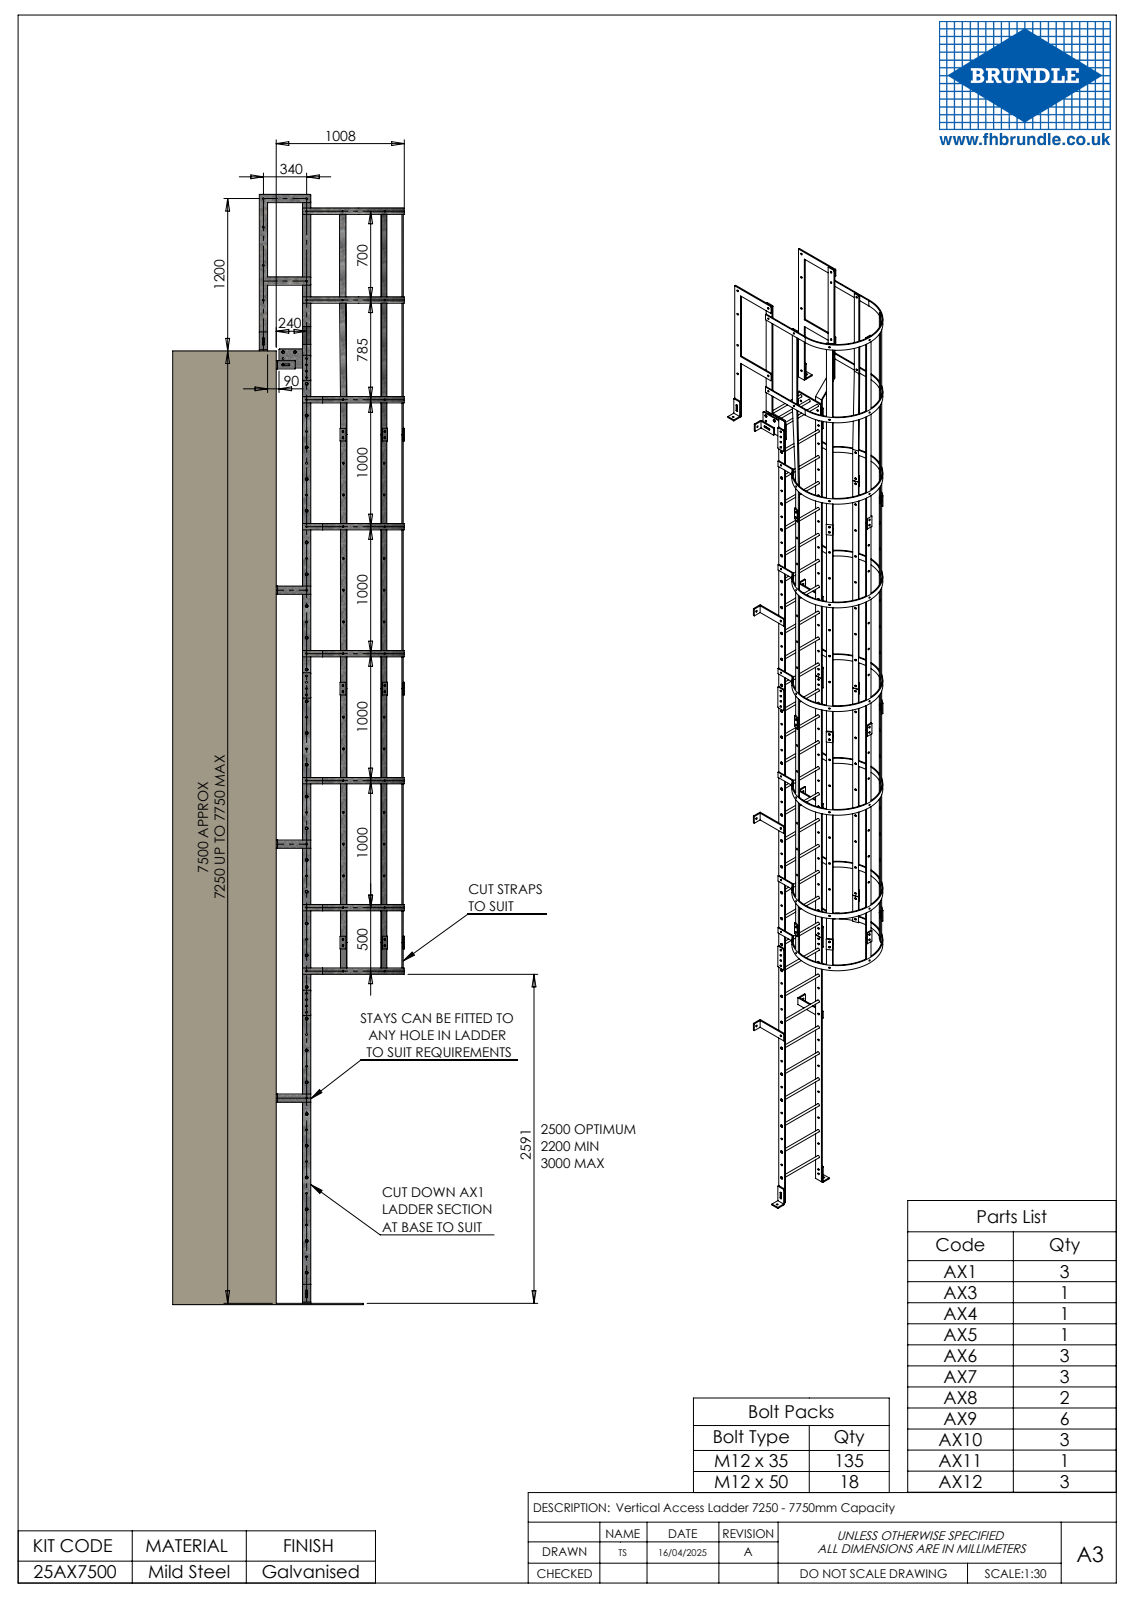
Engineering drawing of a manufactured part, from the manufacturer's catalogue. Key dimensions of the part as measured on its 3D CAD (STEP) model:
Part name (STEP PRODUCT): 25AX6; 25AX10; 25AX9; 25AX12 (+8 more)
STEP written by: SolidWorks 2023 (CONFIG_CONTROL_DESIGN)
Units: millimetres
Bodies: 105 solids, 1592 faces (582 planar, 1002 cylindrical, 8 other)
Overall size (bounding box): 8733 × 1142 × 870
Volume: 43 360 000 mm³ · Surface area: 10 740 000 mm²
Round holes (diameter × count): ⌀15 ×180, ⌀12 ×46, ⌀20 ×32, ⌀14 ×6, ⌀700 ×1
Partial cylindrical surfaces — rounded edges, fillets, slot ends (radius × count): R5 ×22, R2 ×6, R7 ×6, R10 ×6, R358 ×2, R350 ×1
Main face-to-face distances: 10, 410, 140, 560, 150, 550, 420, 400, 0.5, 20
Hole centre spacings: 250, 500, 1000, 750, 1250, 2000, 1500, 1750
